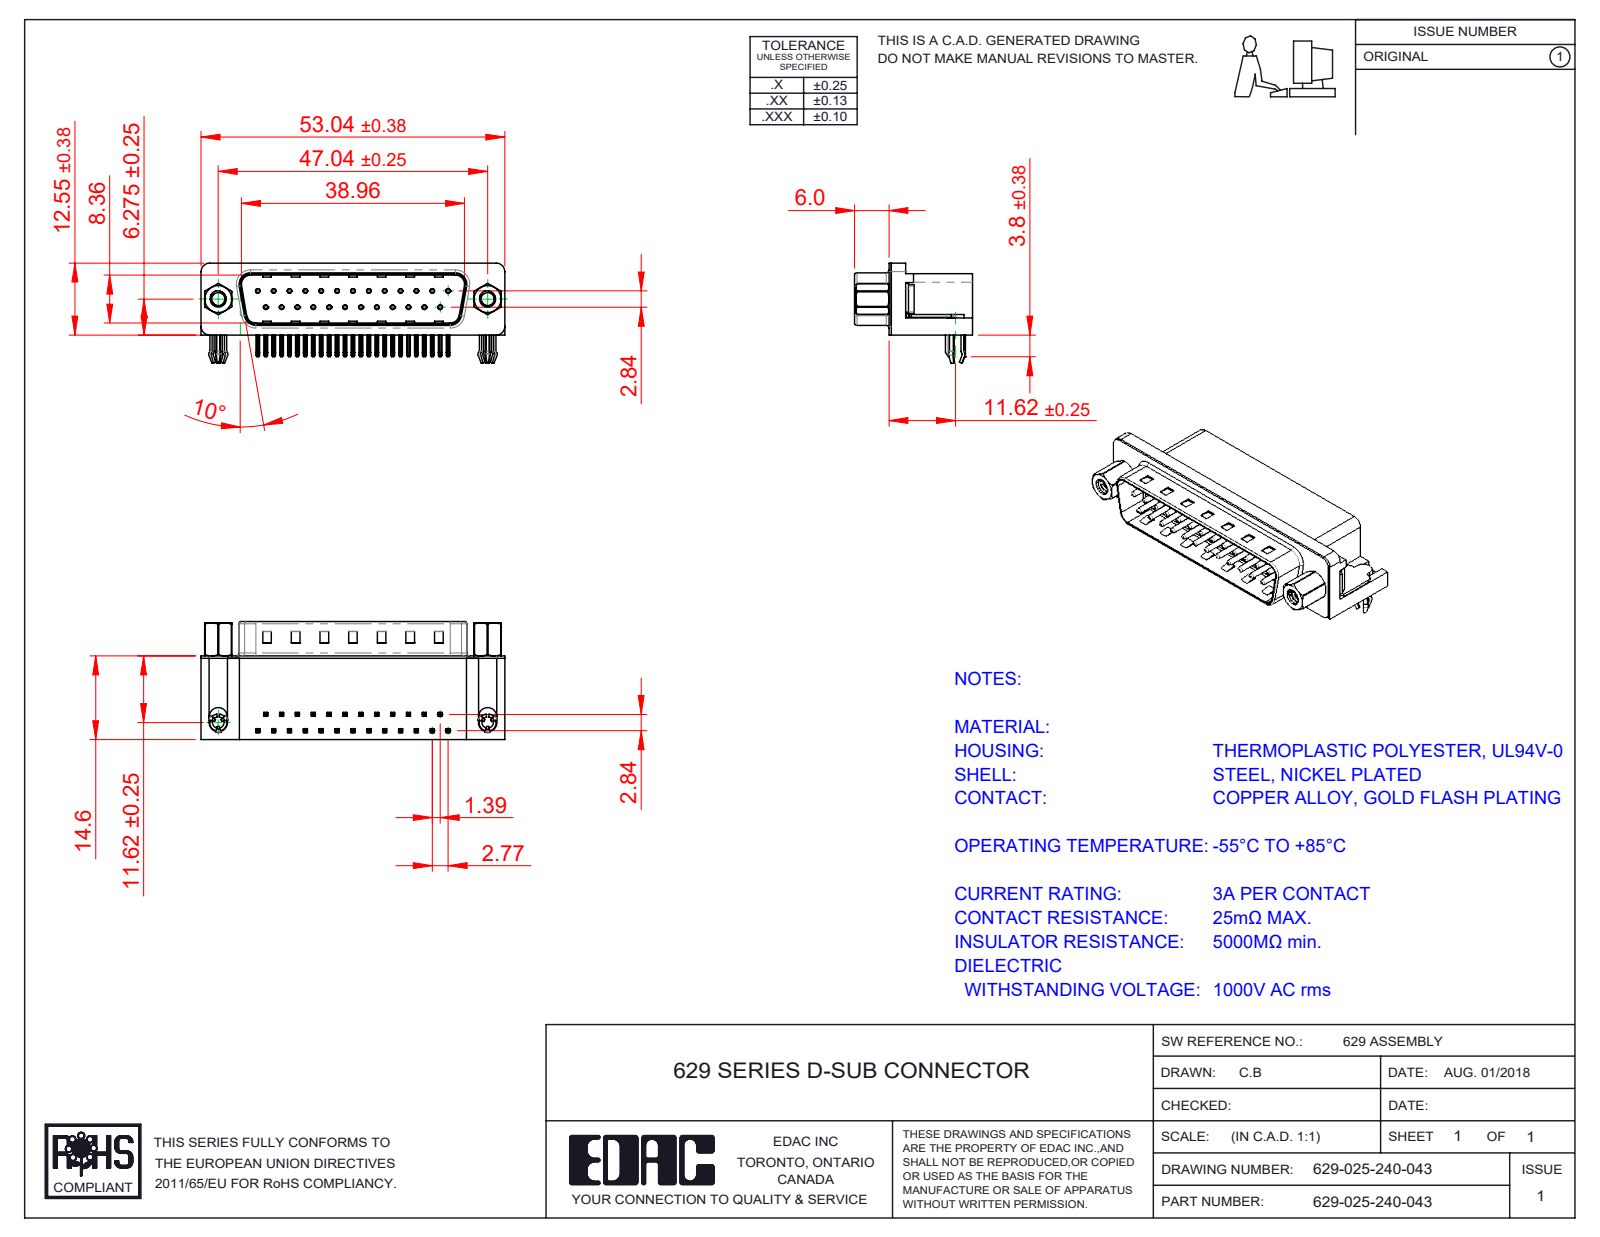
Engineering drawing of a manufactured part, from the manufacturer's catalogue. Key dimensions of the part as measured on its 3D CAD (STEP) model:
Part name (STEP PRODUCT): 629 Contact Top; 629 4-40 Hex Standoff 5; 629-025-240-043; 629 Contact Bottom (+4 more)
STEP written by: SolidWorks 2020 (CONFIG_CONTROL_DESIGN)
Units: millimetres
Bodies: 33 solids, 2491 faces (1463 planar, 737 cylindrical, 291 other)
Overall size (bounding box): 53.04 × 20.6 × 17.48
Volume: 7 549 mm³ · Surface area: 8 789 mm²
Round holes (diameter × count): ⌀0.35 ×25, ⌀0.8 ×25, ⌀2 ×2, ⌀2.26 ×2, ⌀2.29 ×2, ⌀4 ×2, ⌀4.8 ×2, ⌀5 ×2
Round bosses / shafts (diameter × count): ⌀0.75 ×25, ⌀4.9 ×2, ⌀4.75 ×2, ⌀3.9 ×2, ⌀3 ×2, ⌀2.79 ×2
Partial cylindrical surfaces — rounded edges, fillets, slot ends (radius × count): R0.25 ×112, R0.12 ×50, R1 ×16, R0.5 ×9, R1.6 ×8, R1.5 ×7, R0.9 ×4, R2 ×4
Main face-to-face distances: 0.4, 10.36, 14.2, 2.1, 8.76, 14.6, 1.7, 10.46, 10.86, 2.9
Hole centre spacings: 3.16, 2.77, 5.54, 8.31, 11.08, 13.85, 16.62, 5.03
